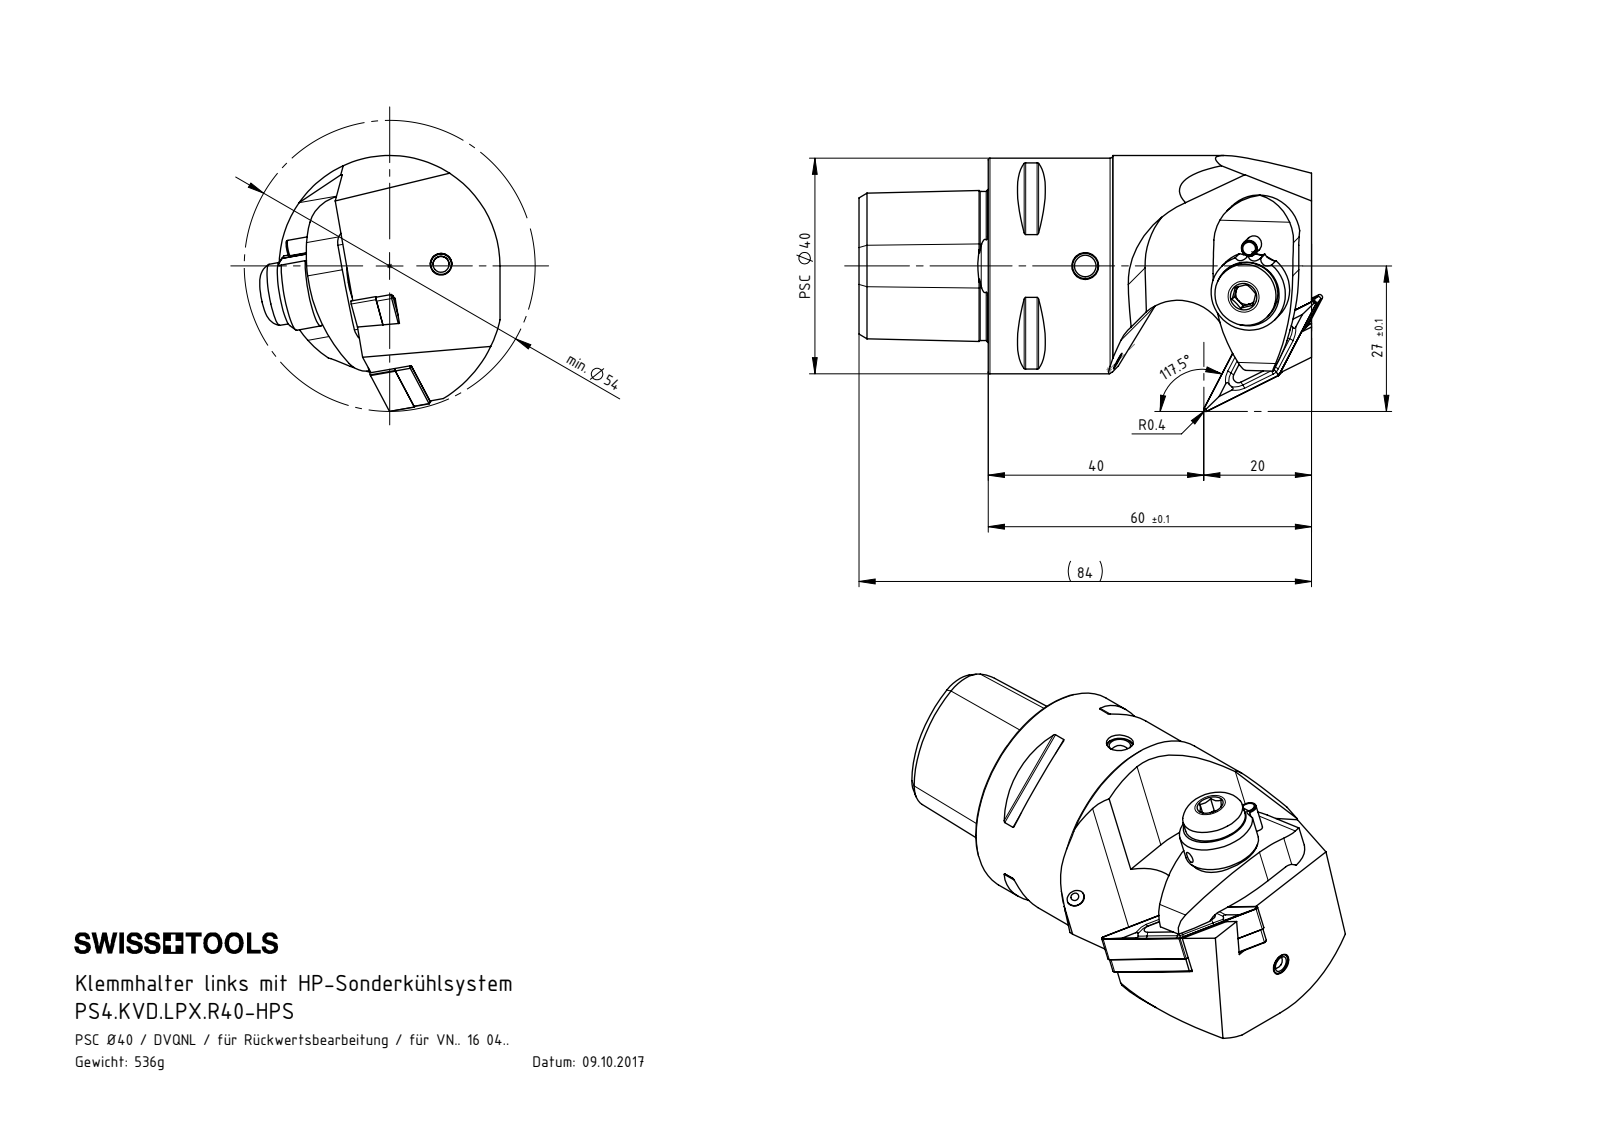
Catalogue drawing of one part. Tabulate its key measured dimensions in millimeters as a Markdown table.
| quantity | value |
| --- | --- |
| part name | KVT_MB_600_050; ISO 13337 - 3 x 12_PreviewCfg; VNMG160404; WVD-ER2.101.003_A (+7 more) |
| STEP written by | SolidWorks 2022 (AUTOMOTIVE_DESIGN) |
| units | millimeters |
| bodies | 14 solids, 375 faces (110 planar, 105 cylindrical, 160 other) |
| overall size | 89 × 47.5 × 45.09 |
| volume | 71 282 mm³ |
| surface area | 22 088 mm² |
| round holes (diameter × count) | 2 × 4, 3.3 × 3, 3 × 2, 4 × 2, 4.2 × 2, 5 × 2, 6.2 × 2, 7 × 2, 1.5 × 1, 2.4 × 1, 3.8 × 1, 4.6 × 1 |
| round bosses / shafts (diameter × count) | 4 × 3, 5 × 2, 3 × 2, 40 × 1, 14 × 1, 11.5 × 1, 6.8 × 1, 6.2 × 1 |
| partial cylindrical surfaces (radius × count) | 0.3 × 8, 0.34 × 6, 0.59 × 6, 0.4 × 4, 1.5 × 3, 3 × 3, 0.8 × 2, 2 × 2 |
| main face-to-face distances | 65, 4.53, 7.71, 3.18, 28.01, 9.23, 1.3, 5.83, 9.01, 24 |
| hole center spacings | 8.2, 8.02, 8.03, 14.08, 14.12, 14.3, 22.32, 6 |
